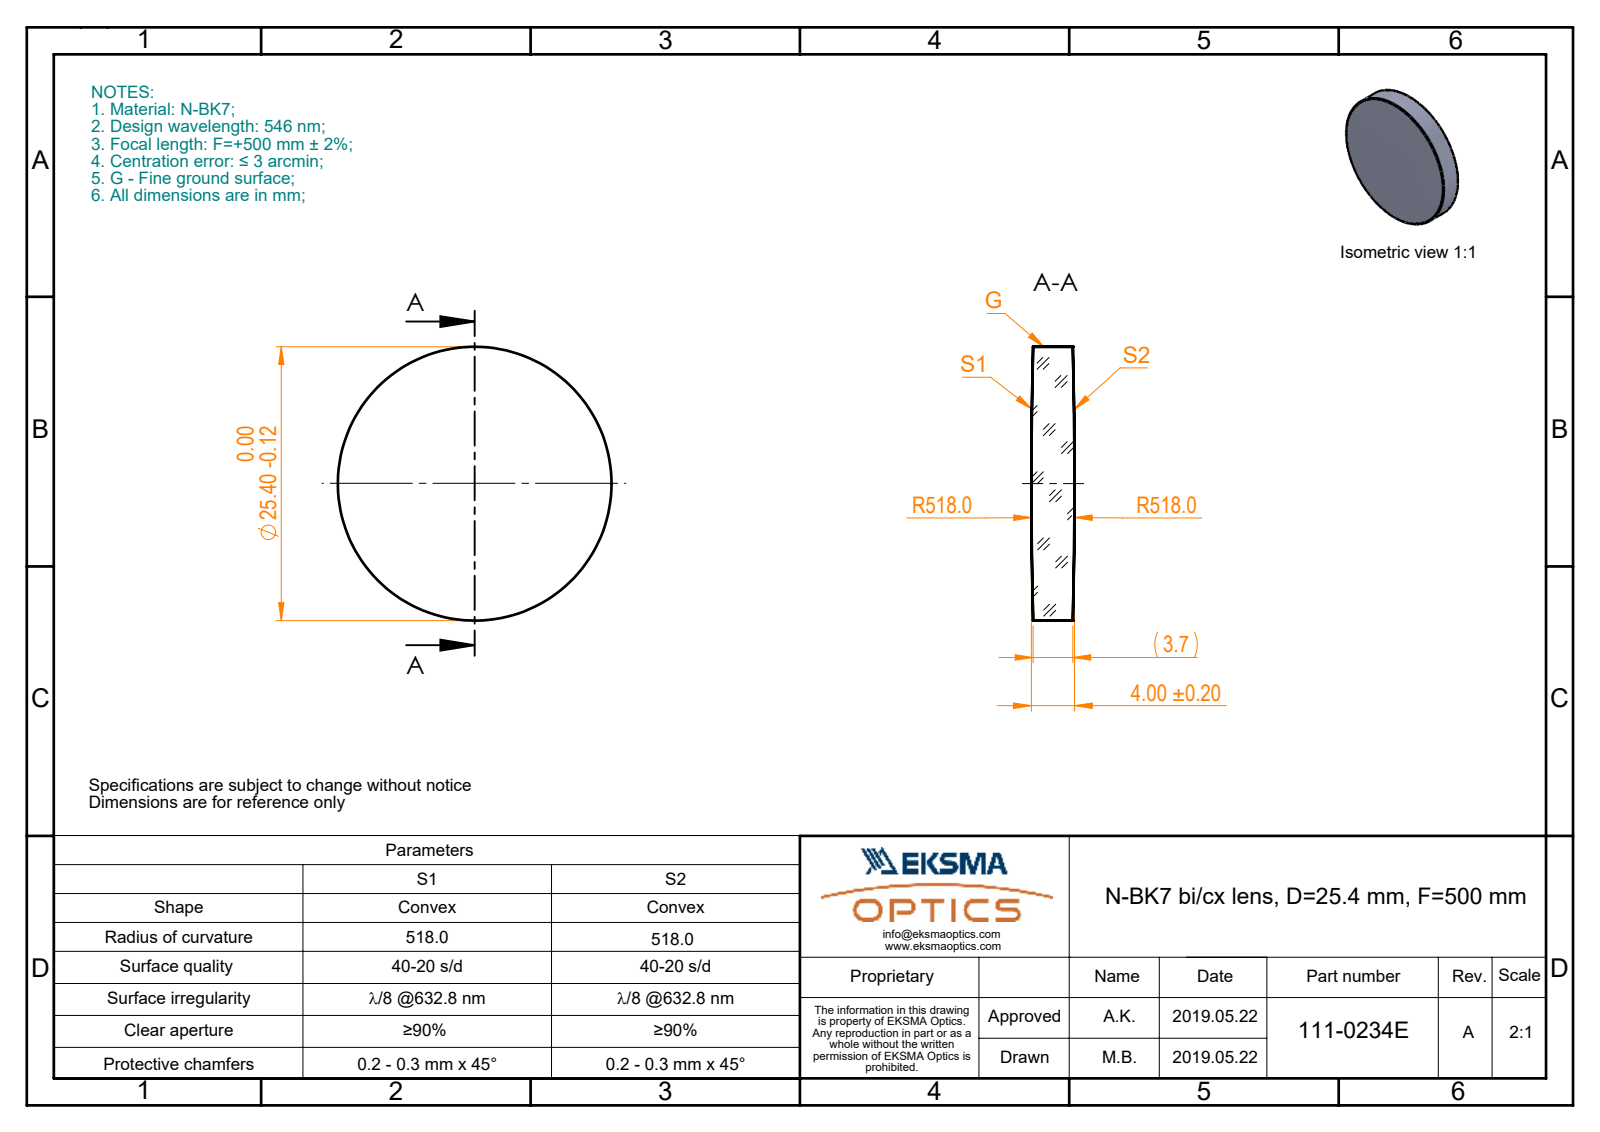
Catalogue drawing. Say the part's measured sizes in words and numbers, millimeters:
The part is named "111-0234E BK7 bi-cx 25.4 F500". Its 3-D file was written by "SolidWorks 2017 (CONFIG_CONTROL_DESIGN)". It is 1 solid with 6 faces: 0 planar, 2 cylindrical and 4 other. Overall it measures 25.4 by 25.4 by 4 millimeters. Its volume is 1 948 cubic millimeters and its surface area 1 308 square millimeters. Round bosses or shafts: 1 of diameter 25.4.
